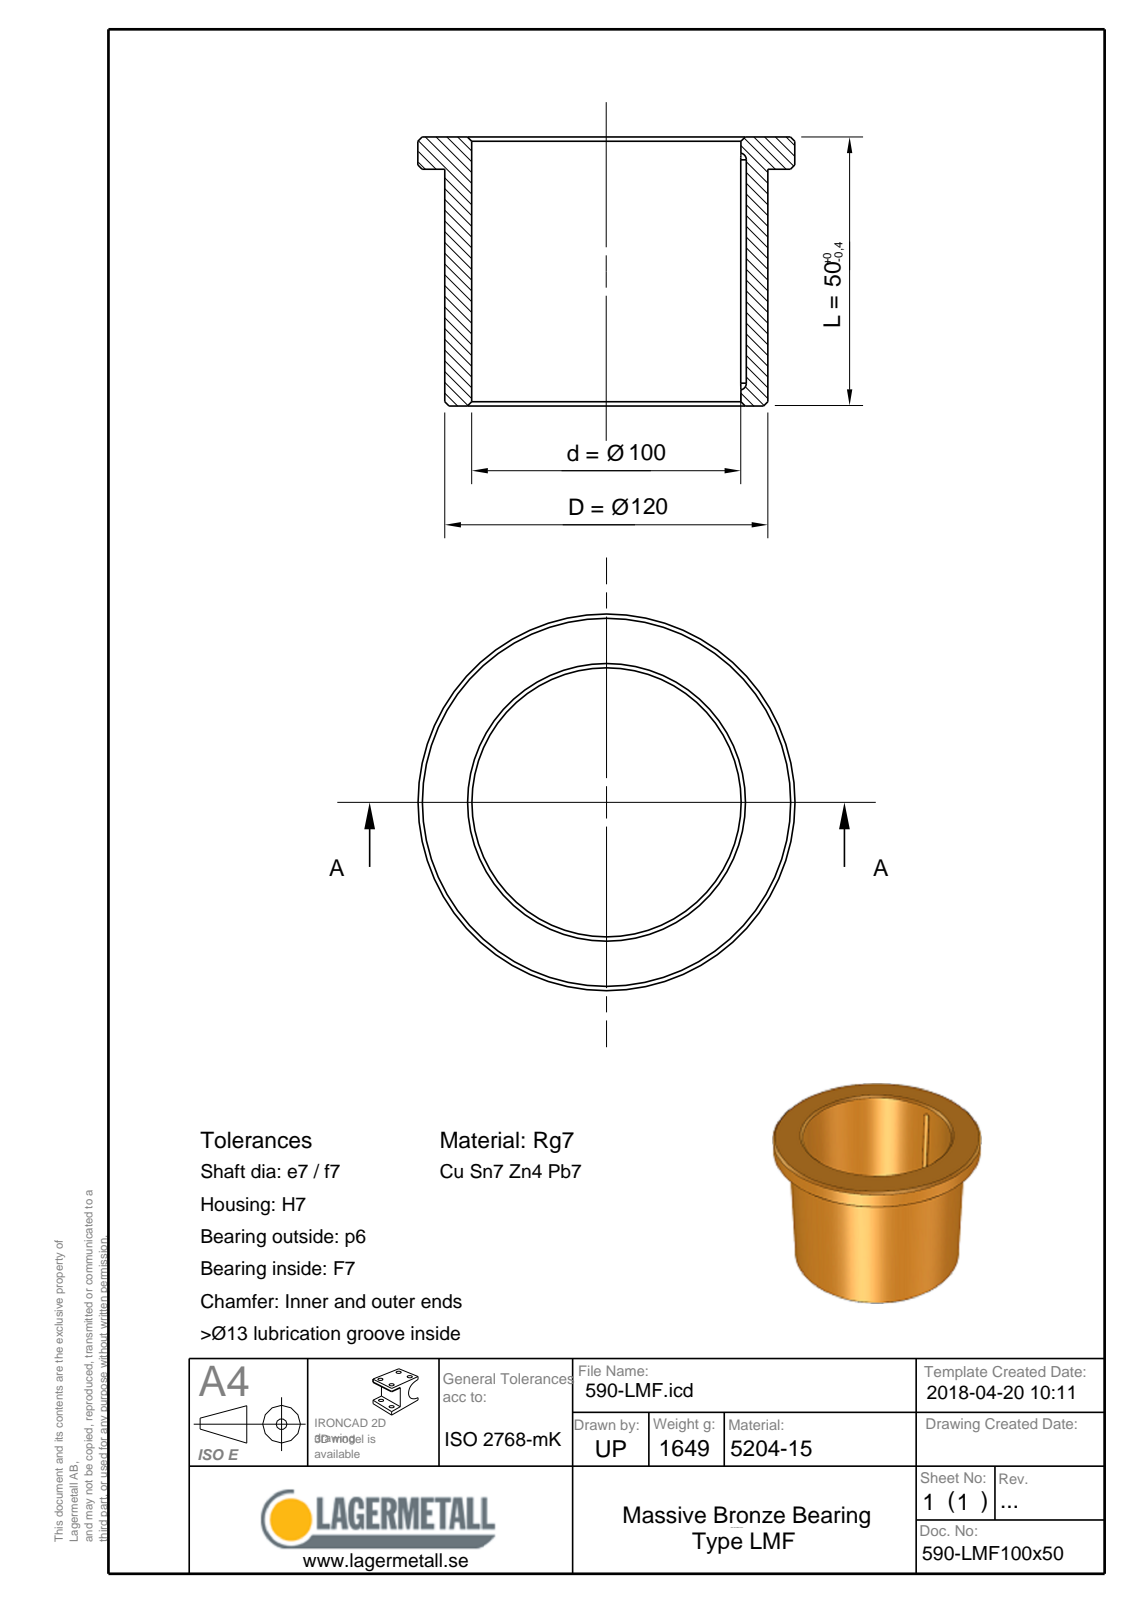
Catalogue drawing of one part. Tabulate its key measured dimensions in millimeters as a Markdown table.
| quantity | value |
| --- | --- |
| part name | 590-LMF100x50 |
| STEP written by | Spatial InterOp 3D (CONFIG_CONTROL_DESIGN) |
| units | millimeters |
| bodies | 1 solid, 16 faces (4 planar, 5 cylindrical, 7 other) |
| overall size | 130 × 130 × 50 |
| volume | 187 422 mm³ |
| surface area | 44 647 mm² |
| round holes (diameter × count) | 100 × 1 |
| round bosses / shafts (diameter × count) | 130 × 1, 120 × 1 |
| partial cylindrical surfaces (radius × count) | 1.75 × 2 |
| main face-to-face distances | 50, 42, 8 |
